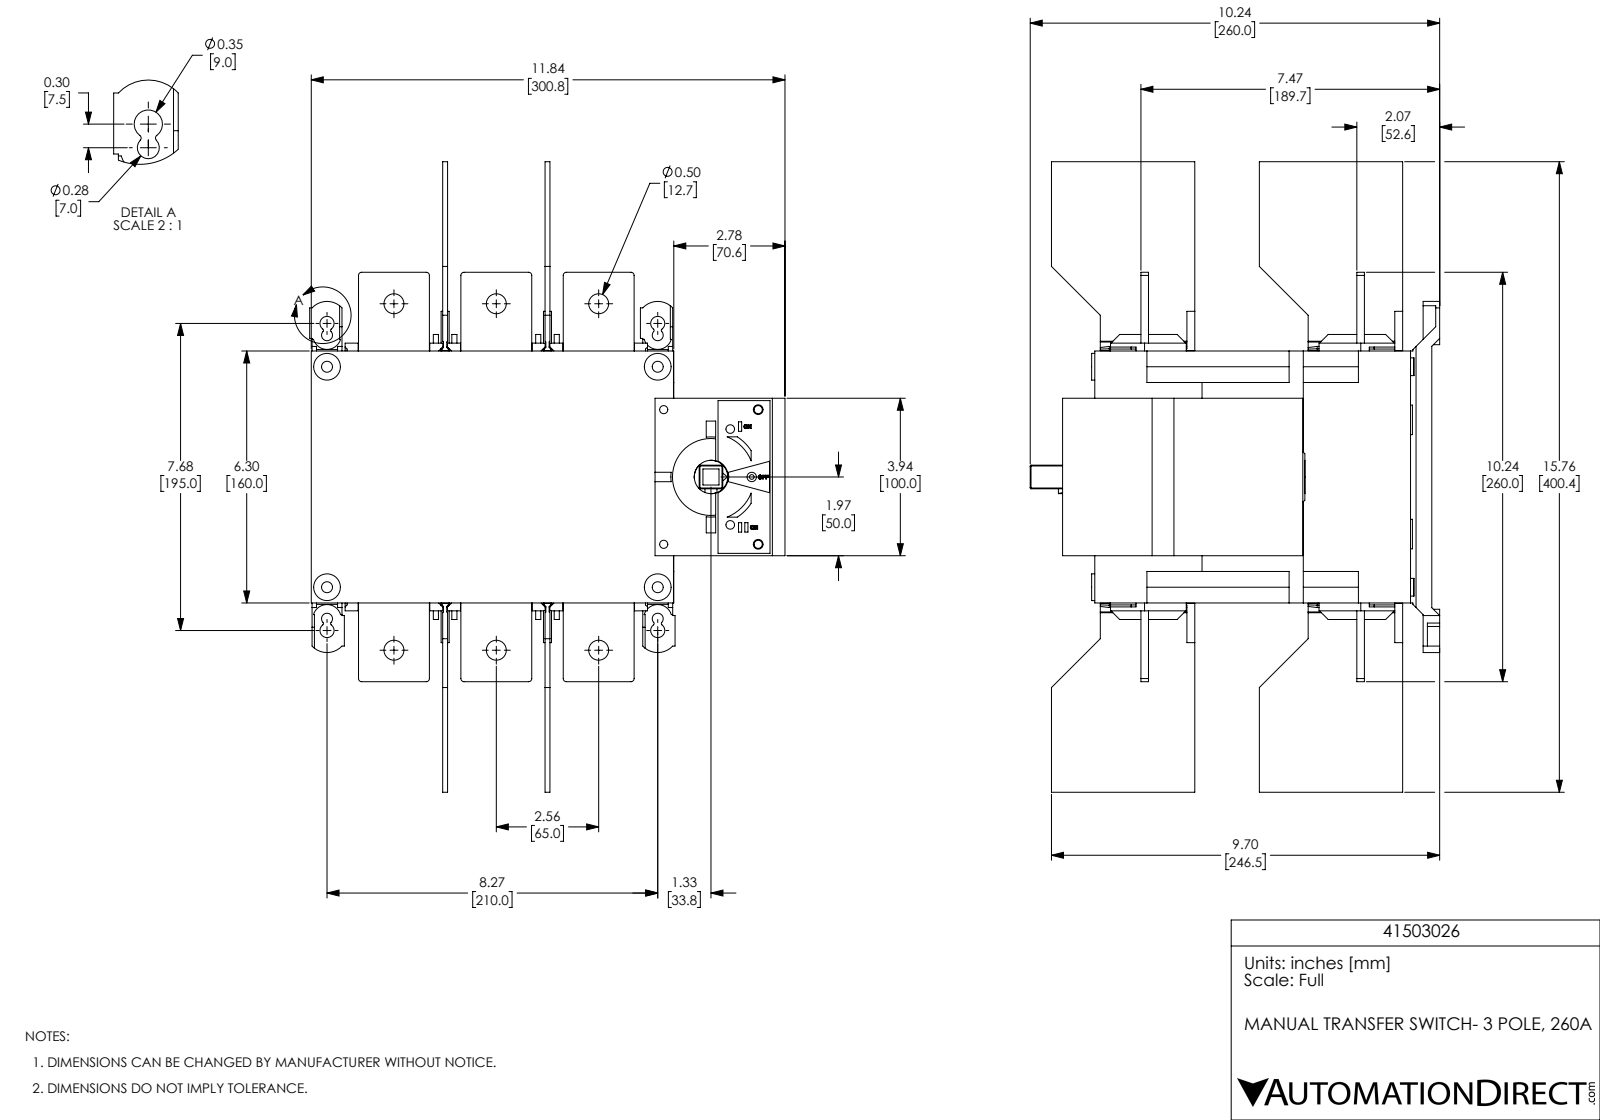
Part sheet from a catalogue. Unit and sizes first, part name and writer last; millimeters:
Units: millimetres
Overall size (bounding box): 400.4 × 301.8 × 260
Round holes (diameter × count): ⌀6.3 ×12, ⌀12.7 ×6, ⌀5.2 ×4, ⌀7 ×4, ⌀9 ×4, ⌀12 ×4, ⌀5.5 ×2, ⌀3 ×1, ⌀21.3 ×1, ⌀21.5 ×1
Round bosses / shafts (diameter × count): ⌀17 ×4, ⌀21.2 ×1, ⌀6 ×1
Partial cylindrical surfaces — rounded edges, fillets, slot ends (radius × count): R2 ×12, R8.7 ×12, R1 ×8, R5.5 ×8, R0.5 ×4, R1.2 ×4, R3.5 ×4, R6 ×4
Main face-to-face distances: 3.1, 65, 68.1, 61.9, 160, 200.5, 83.4, 4.8, 86.5, 148.4
Hole centre spacings: 65, 210, 52.2, 229.4, 130, 27.5, 32.8, 131.1
Volume: 8 062 000 mm³ · Surface area: 652 300 mm²
Bodies: 11 solids, 1480 faces (1182 planar, 292 cylindrical, 6 other)
Part name (STEP PRODUCT): 41503026
STEP written by: SolidWorks 2017 (AUTOMOTIVE_DESIGN)
